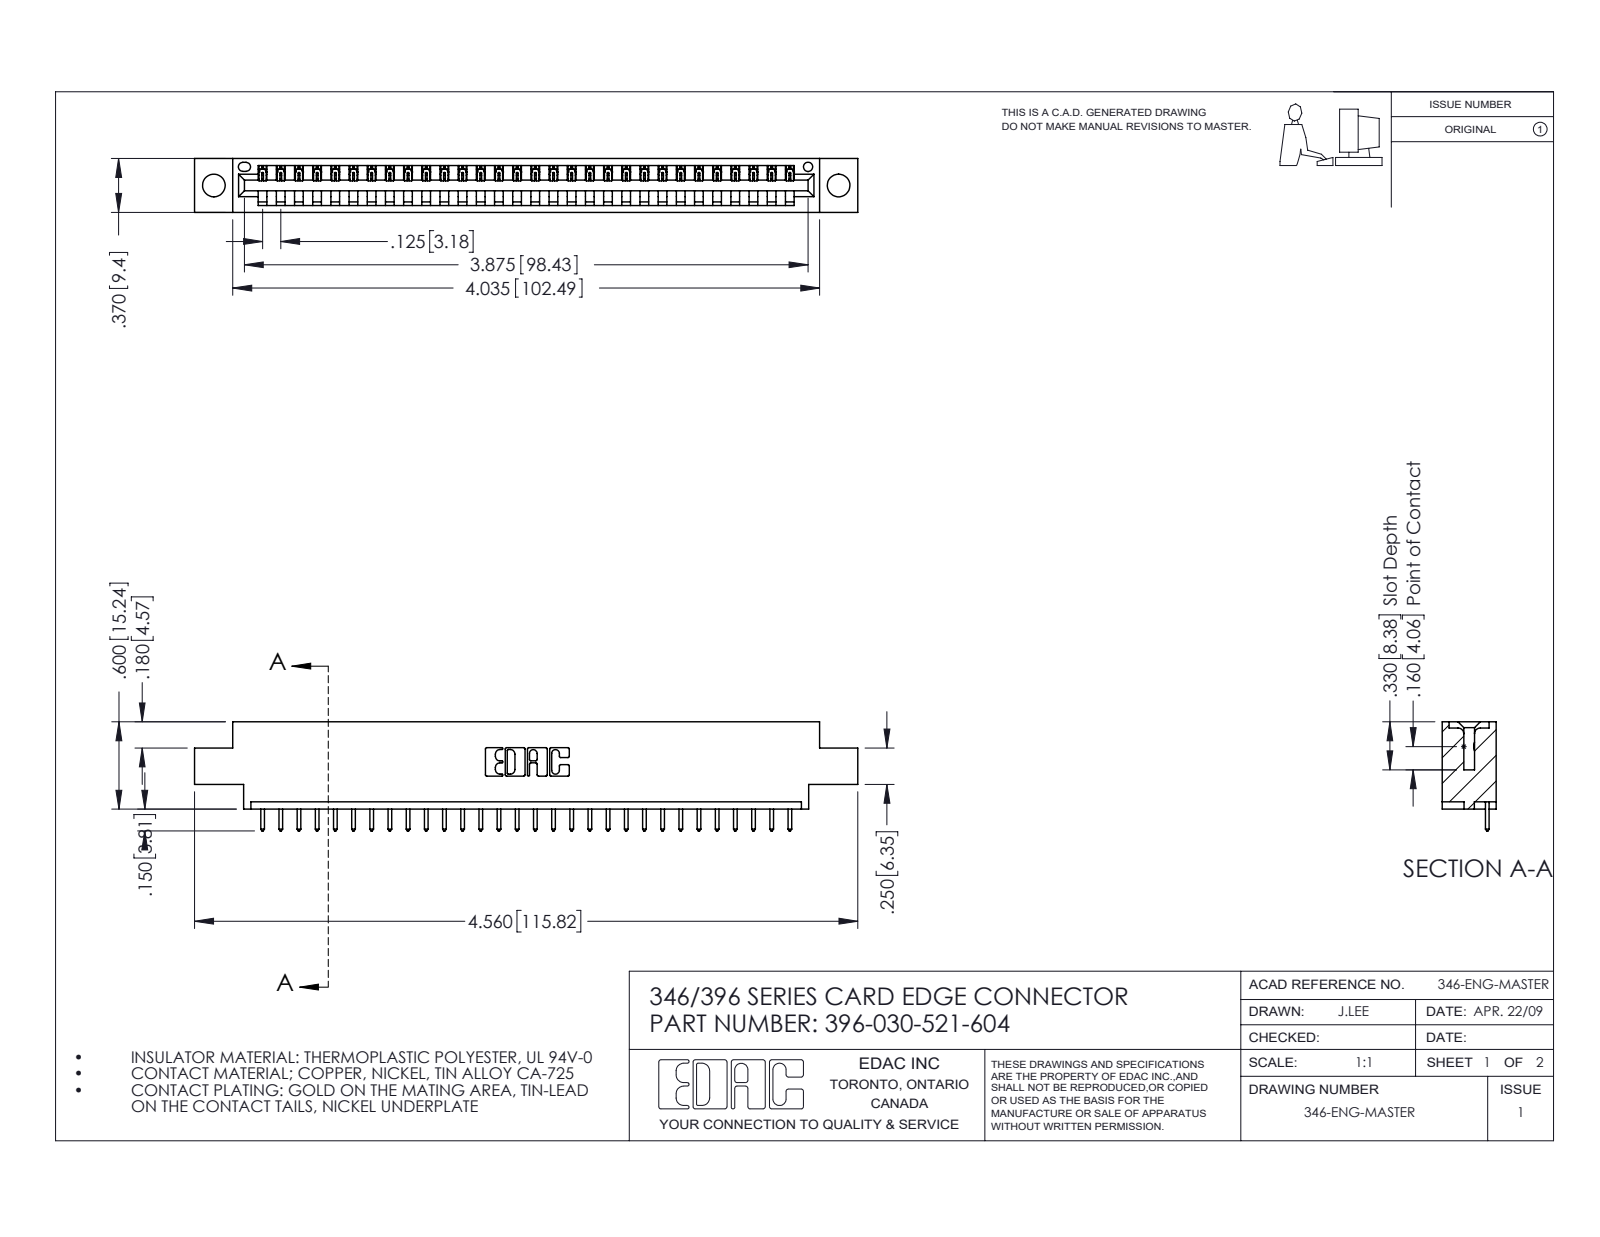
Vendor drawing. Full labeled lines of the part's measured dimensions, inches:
Part name (STEP PRODUCT): 396-030-521-604; 346 Part_0.170 Offset - 0.156 Dia-TH; 345-292-001_345-293-121
STEP written by: SolidWorks 2016 (CONFIG_CONTROL_DESIGN)
Units: inches
Bodies: 31 solids, 1866 faces (1280 planar, 586 cylindrical, 0 other)
Overall size (bounding box): 4.56 × 0.75 × 0.37
Volume: 0.652 in³ · Surface area: 19.9 in²
Round holes (diameter × count): ⌀0.156 ×2, ⌀0.064 ×1
Partial cylindrical surfaces — rounded edges, fillets, slot ends (radius × count): R0.006 ×60, R0.01 ×60, R0.01 ×22, R0.007 ×6, R0.031 ×6, R0.026 ×3, R0.031 ×2, R0.04 ×2
Main face-to-face distances: 0.048, 0.322, 0.37, 0.25, 0.072, 0.298, 0.025, 0.148, 0.222, 0.1
Hole centre spacings: 0.246, 4.087, 4.295
